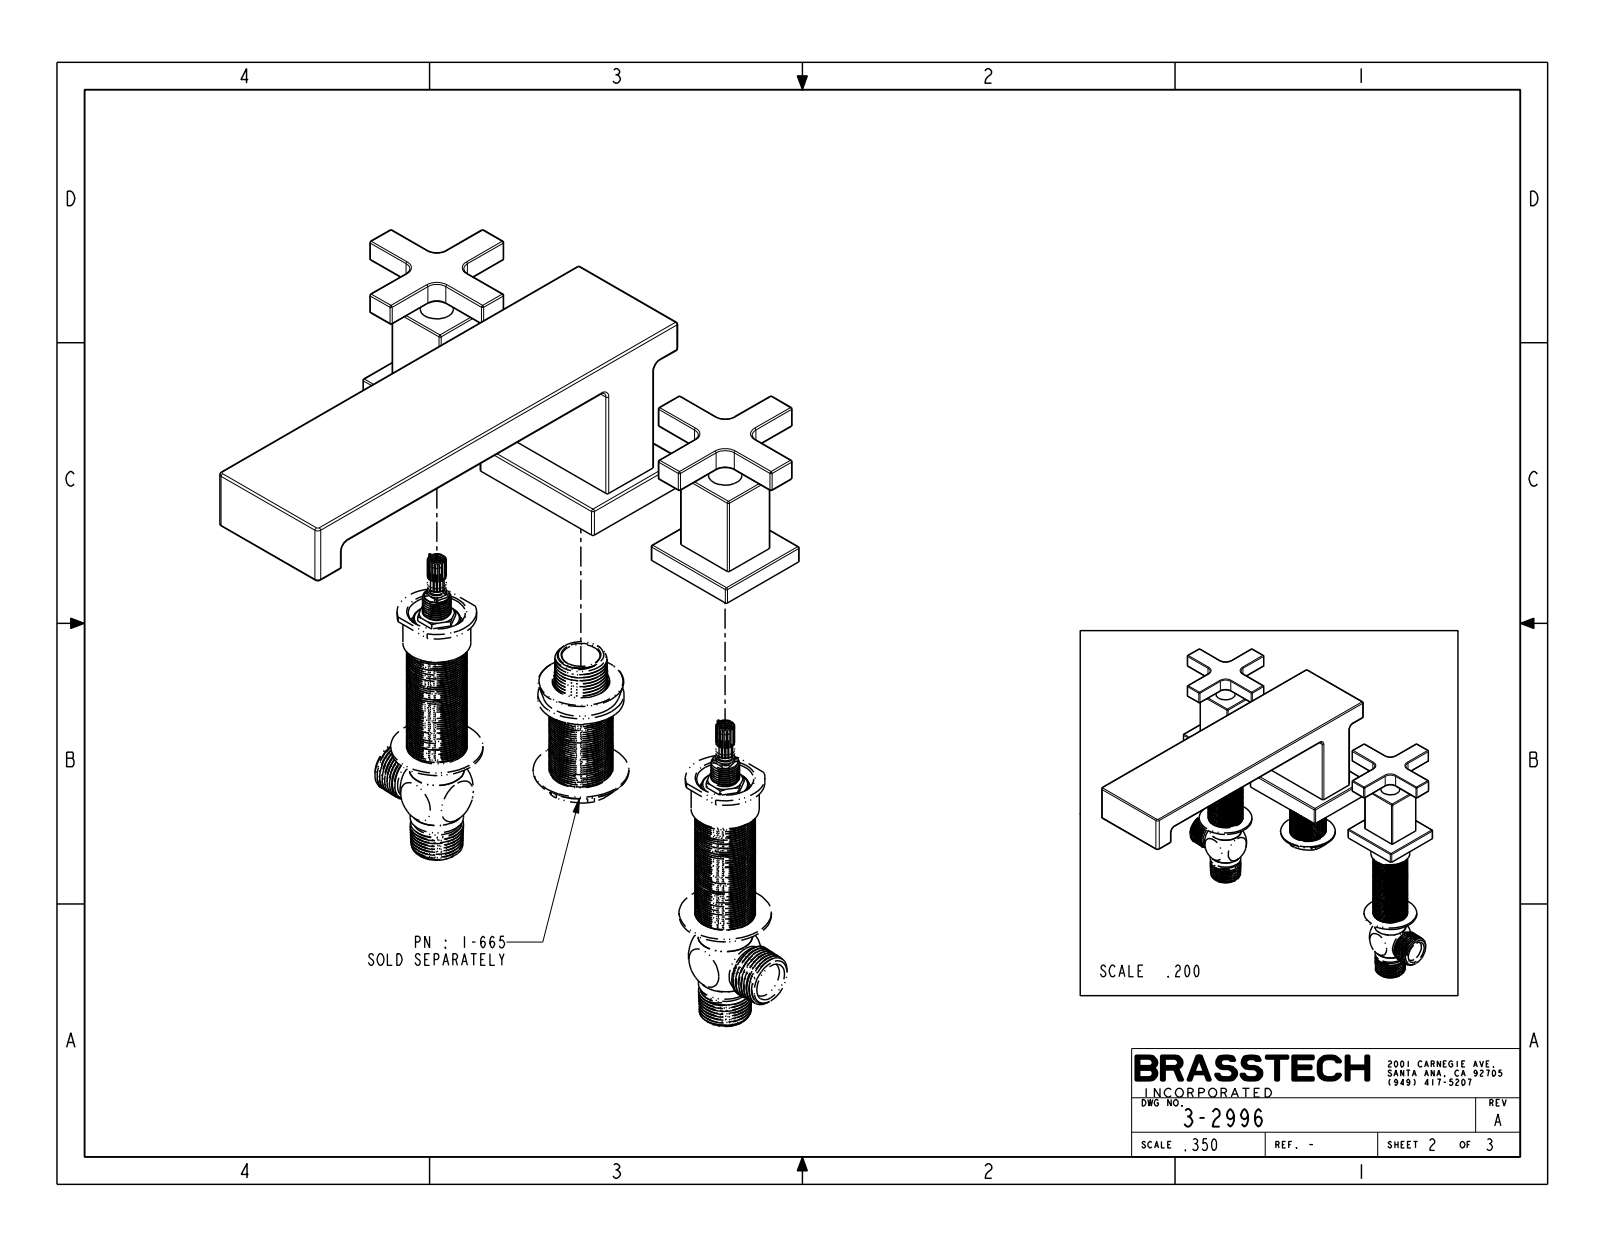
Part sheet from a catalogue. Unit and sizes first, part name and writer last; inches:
Units: inches
Overall size (bounding box): 11.14 × 10.251 × 3.76
Round bosses / shafts (diameter × count): ⌀0.65 ×2, ⌀0.523 ×2
Partial cylindrical surfaces — rounded edges, fillets, slot ends (radius × count): R0.03 ×68, R0.04 ×27, R0.25 ×8, R0.16 ×3, R0.08 ×2
Main face-to-face distances: 0.67, 3.09, 3.76, 2.76, 0.07, 1.23, 0.35, 8, 1.3, 3.046
Volume: 44.91 in³ · Surface area: 174.3 in²
Bodies: 3 solids, 303 faces (69 planar, 146 cylindrical, 88 other)
Part name (STEP PRODUCT): 3-2996
STEP written by: CREO PARAMETRIC BY PTC INC, 2018400 (CONFIG_CONTROL_DESIGN)
